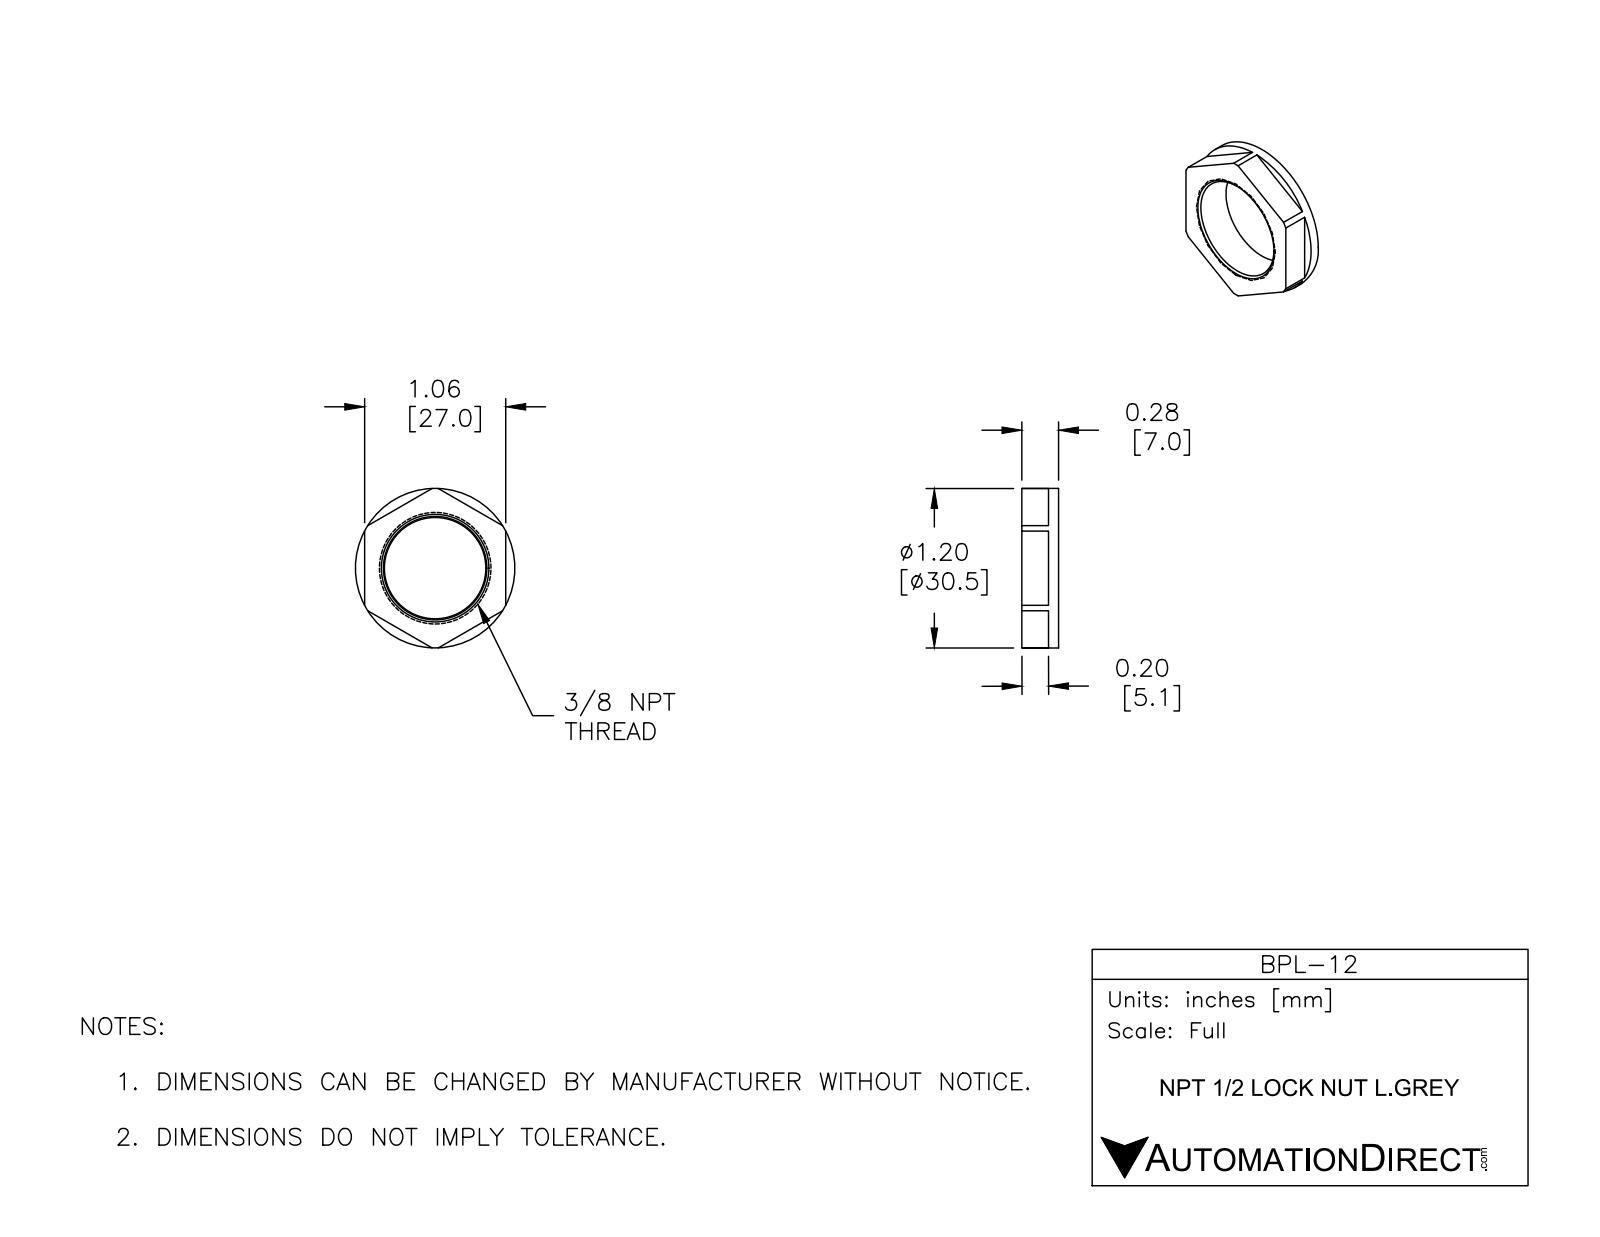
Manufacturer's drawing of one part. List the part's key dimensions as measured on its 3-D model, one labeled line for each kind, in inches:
Part name (STEP PRODUCT): BPL-12
STEP written by: SolidWorks 2015 (CONFIG_CONTROL_DESIGN)
Units: inches
Bodies: 1 solid, 20 faces (14 planar, 2 cylindrical, 4 other)
Overall size (bounding box): 1.2 × 1.2 × 0.276
Volume: 0.152 in³ · Surface area: 2.989 in²
Round bosses / shafts (diameter × count): ⌀1.2 ×1
Main face-to-face distances: 0.276, 1.062, 0.076, 0.2
